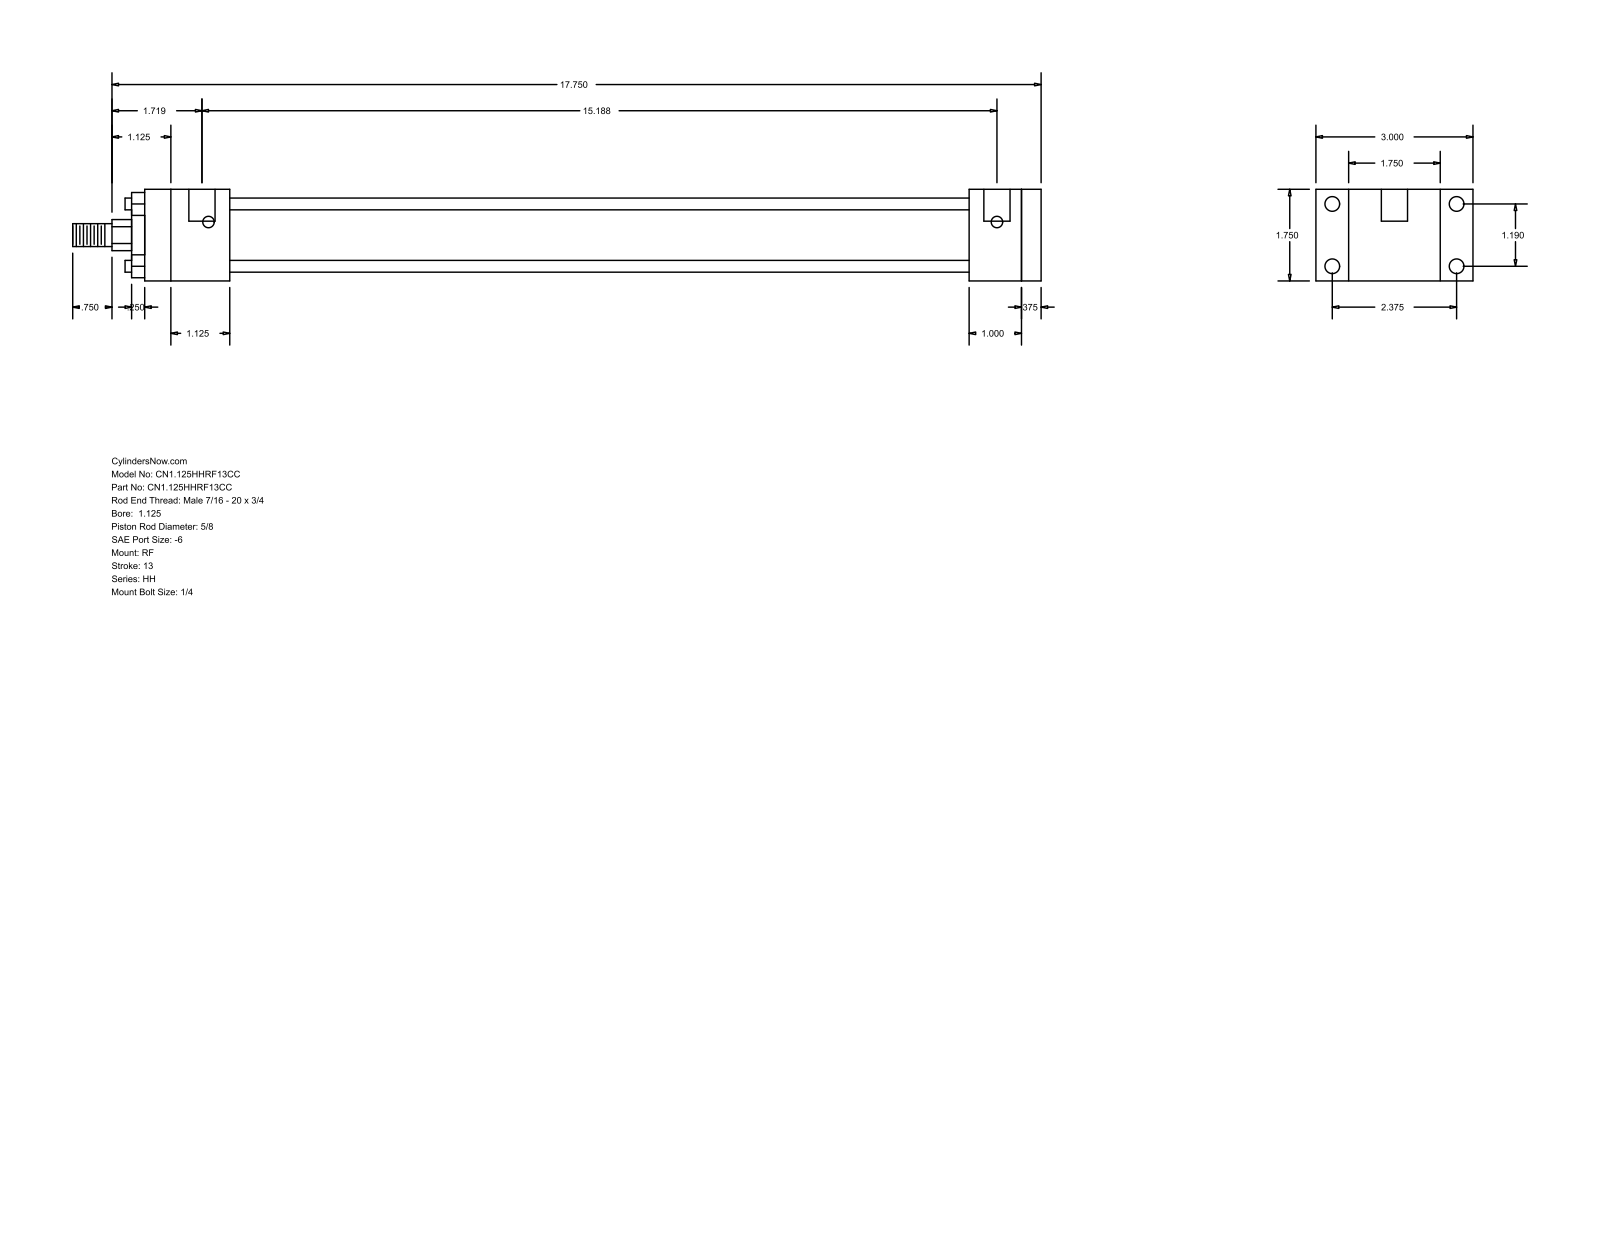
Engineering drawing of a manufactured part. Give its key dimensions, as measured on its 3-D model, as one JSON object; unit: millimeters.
{"part_name": "HH_RF__0112_0.625", "step_written_by": "GSSL Pune (CONFIG_CONTROL_DESIGN)", "units": "millimeters", "bodies": {"solids": 0, "faces": 92, "planar": 64, "cylindrical": 28, "other": 0}, "overall_size": [469.9, 76.2, 44.45], "round_holes": [[5.56, 4], [7.14, 4], [12.7, 2]], "round_bosses_or_shafts": [[5.71, 4], [34.92, 1], [28.57, 1], [15.88, 1], [11.11, 1]], "partial_cylinders_radius": [[7.54, 1]], "face_to_face_distances": [44.46, 9.53, 434.97, 15.87, 384.17, 393.7, 358.78, 25.39, 34.92, 41.27], "hole_center_spacings": [30.22, 60.32, 67.47, 382.59, 3.17, 385.76]}
